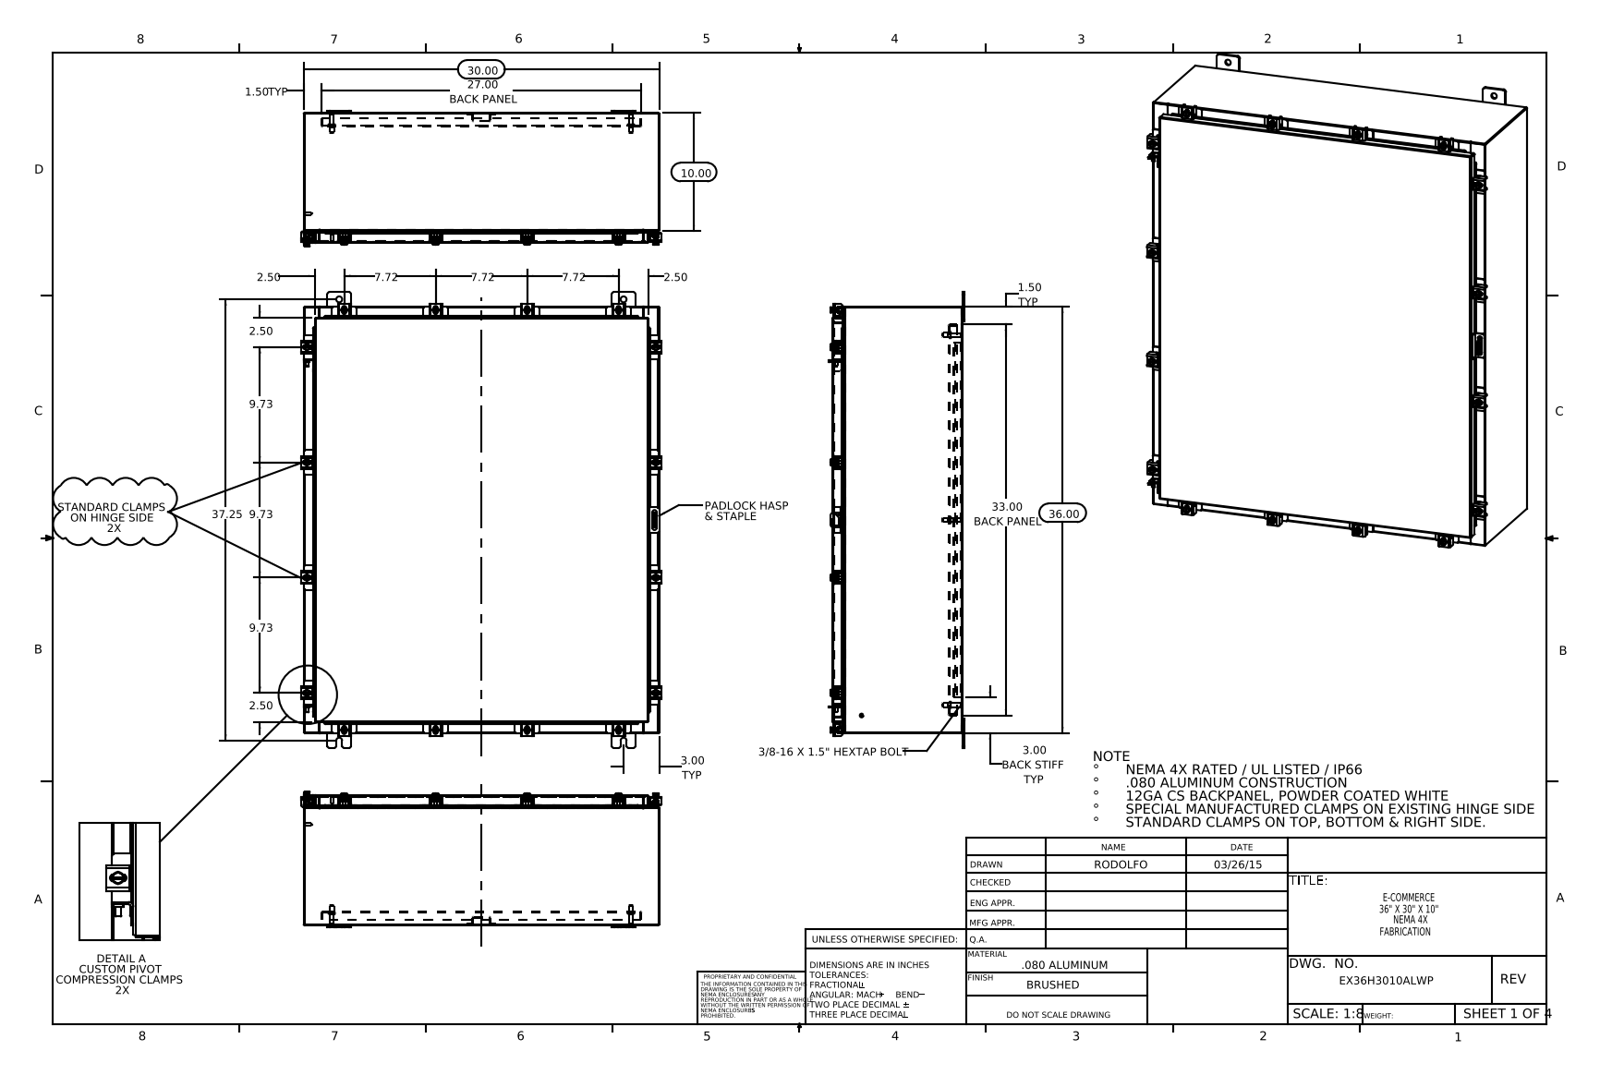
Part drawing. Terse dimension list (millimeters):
name: EX36H3010ALWP Clamp Bracket; 30X10 Clamp Bracket2; HW-CLN-NH-20330; N-WMT04X30402202210-00 22101002 (+8 more)
written by: SolidWorks 2014 (CONFIG_CONTROL_DESIGN)
unit: mm
bodies: 104 solids, 2594 faces (1371 planar, 1011 cylindrical, 212 other)
size: 977.9 × 772.7 × 290.9
volume: 6 571 000 mm³; area: 6 431 000 mm²
holes: 16× ⌀5.4, 16× ⌀6.6, 10× ⌀12.7, 1× ⌀3.2, 1× ⌀6.4
bosses: 16× ⌀12.7, 16× ⌀6.4, 14× ⌀10.1, 6× ⌀15.9, 6× ⌀9.5, 6× ⌀8.4, 2× ⌀8, 2× ⌀6
rounds: 70× R1.5, 32× R3.6, 30× R0.3, 30× R3, 26× R2.2, 24× R4.8, 22× R2.3, 21× R1.3
face distances: 1.9, 276.9, 275, 278.8, 2.6, 25.4, 27.3, 249.6, 251.5, 29.9
hole spacings: 787.8, 59.6, 112.8, 134.6, 247.1, 278.5, 336.3, 374.5
